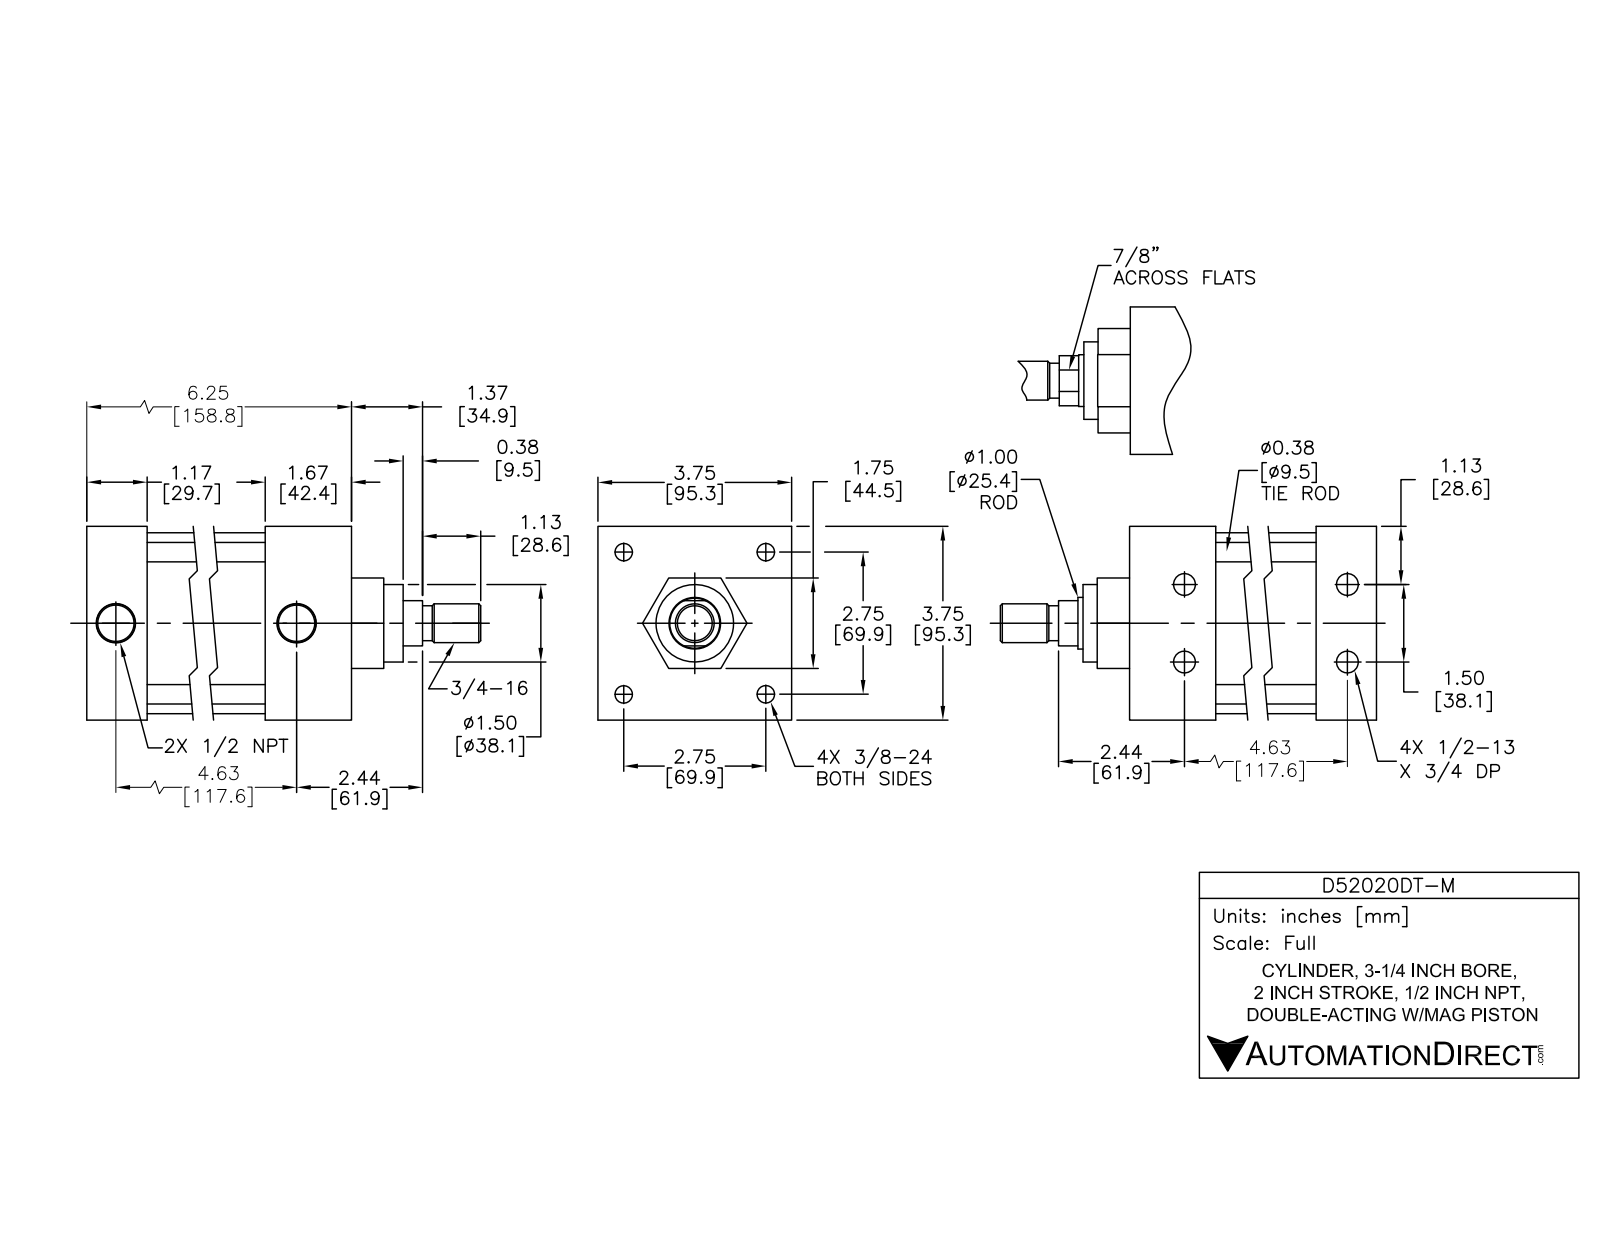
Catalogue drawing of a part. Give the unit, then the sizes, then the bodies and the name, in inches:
Units: inches
Overall size (bounding box): 8.745 × 3.75 × 3.75
Round holes (diameter × count): ⌀0.33 ×4, ⌀0.406 ×4, ⌀0.417 ×4, ⌀0.625 ×4, ⌀0.5 ×2, ⌀0.766 ×2, ⌀1 ×1, ⌀1.003 ×1, ⌀3.25 ×1
Round bosses / shafts (diameter × count): ⌀0.609 ×4, ⌀0.375 ×4, ⌀0.34 ×4, ⌀3.5 ×1, ⌀3.247 ×1, ⌀1.75 ×1, ⌀0.997 ×1, ⌀0.97 ×1
Partial cylindrical surfaces — rounded edges, fillets, slot ends (radius × count): R0.375 ×4
Main face-to-face distances: 3.75, 0.08, 3.326, 6.246, 1.75, 4.997, 1.249, 3.751, 1.246, 2.495
Hole centre spacings: 0.75, 0.76, 1.5, 1.95, 1.95, 2.758, 2.758, 3.9
Volume: 58.77 in³ · Surface area: 294.3 in²
Bodies: 12 solids, 303 faces (99 planar, 114 cylindrical, 90 other)
Part name (STEP PRODUCT): D52020DT-M; D52020DT-M PISTON; D52020DT-M BODY
STEP written by: SolidWorks 2015 (AUTOMOTIVE_DESIGN)
